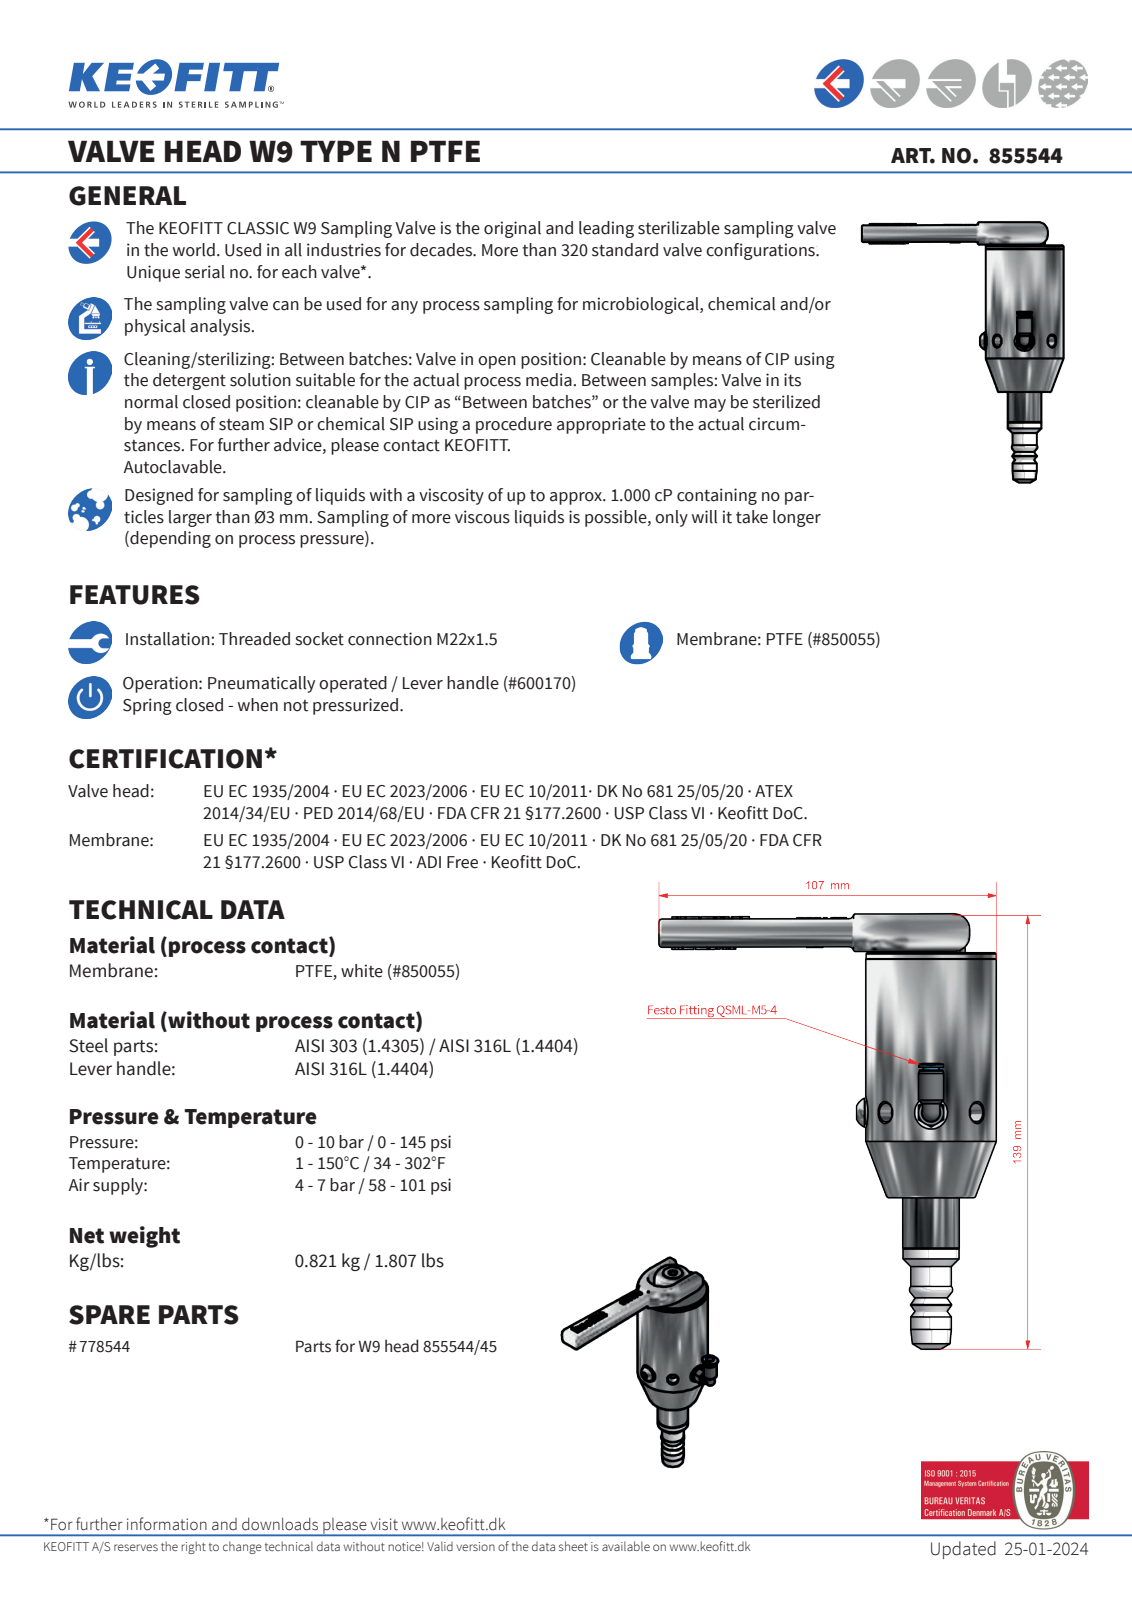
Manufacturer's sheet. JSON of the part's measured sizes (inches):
{"part_name": "600044E_test asm simplify", "step_written_by": "Autodesk Inventor 2022 (AUTOMOTIVE_DESIGN)", "units": "inches", "bodies": {"solids": 3, "faces": 533, "planar": 221, "cylindrical": 69, "other": 243}, "overall_size": [5.843, 5.472, 2.242], "volume_in3": 7.716, "surface_area_in2": 34.91, "round_holes": [[0.157, 1], [0.236, 1]], "round_bosses_or_shafts": [[0.236, 2], [0.22, 2], [1.638, 1], [1.634, 1], [0.709, 1], [0.705, 1], [0.512, 1], [0.315, 1]], "partial_cylinders_radius": [[0.02, 14], [0.008, 10], [0.039, 2], [0.059, 2], [0.154, 2], [0.197, 2], [0.118, 1], [0.146, 1]], "face_to_face_distances": [0.413, 0.059, 0.354, 3.079, 3.138, 3.492, 0.472, 3.551, 0.079, 0.589]}
